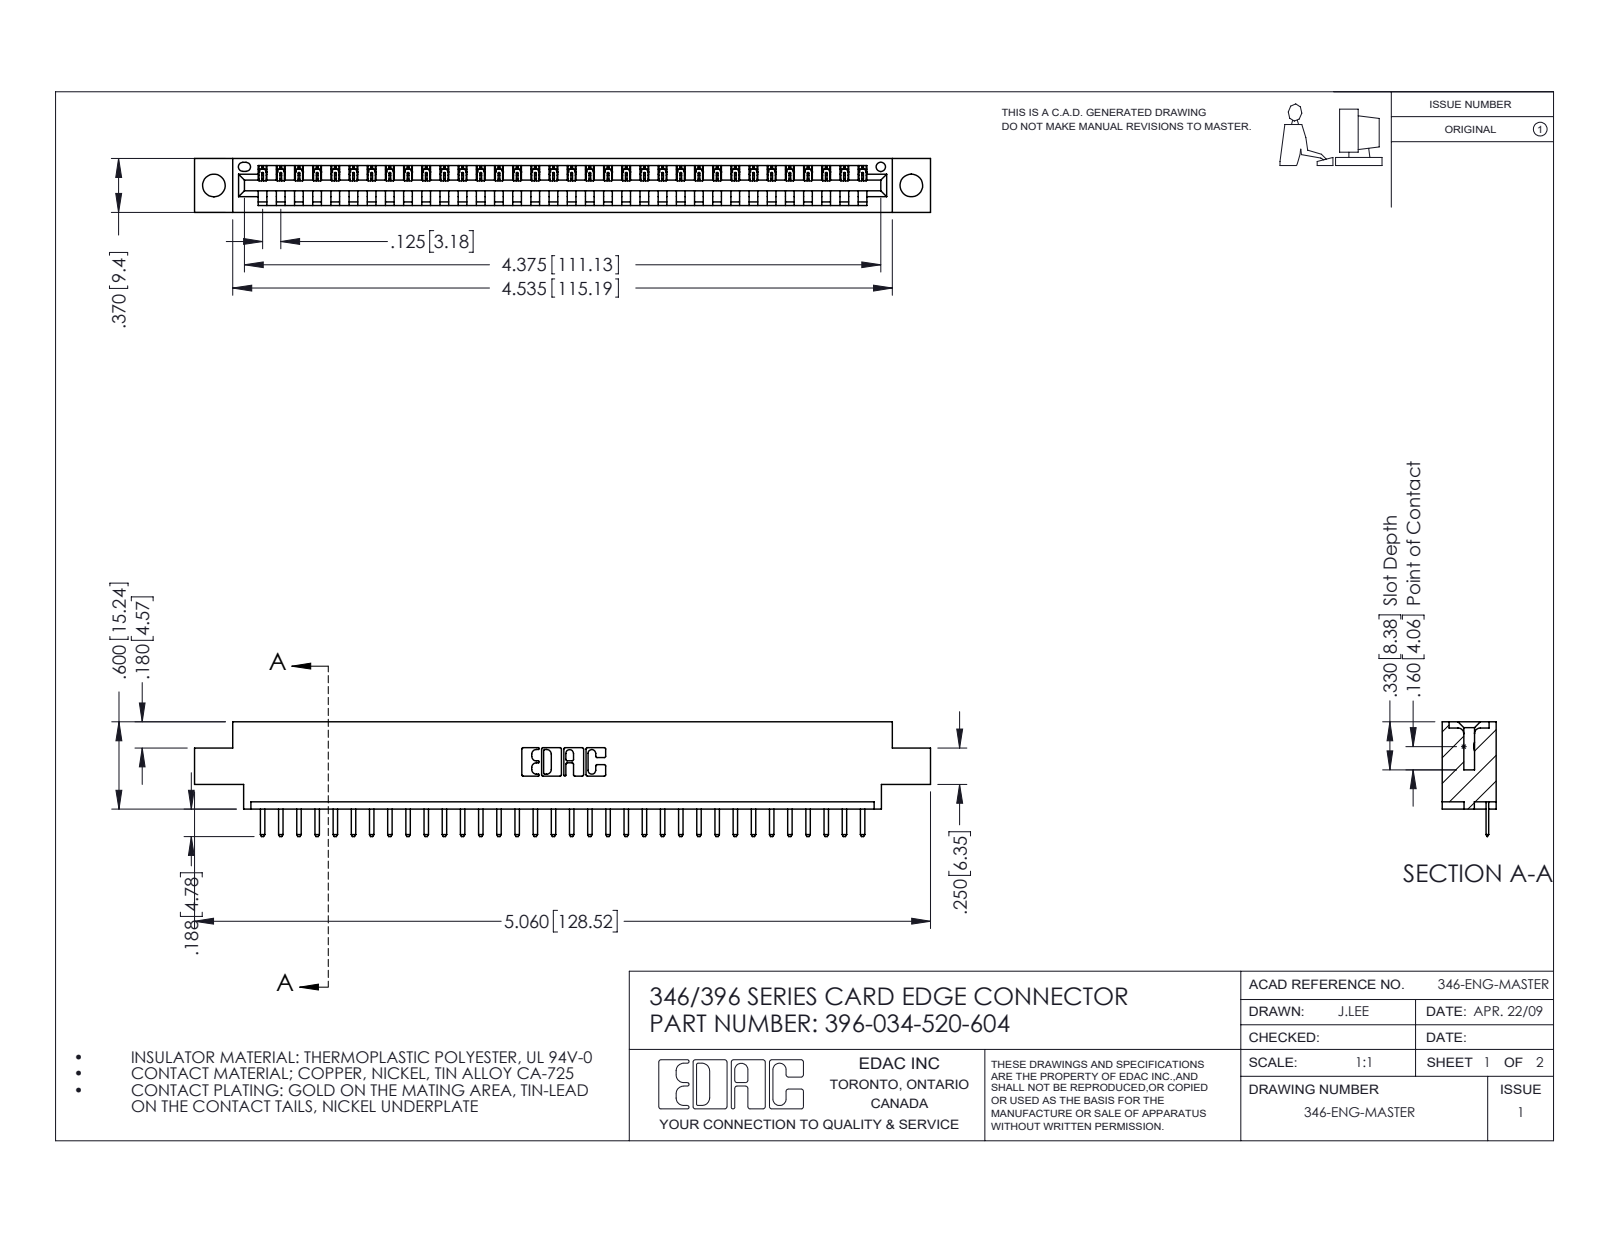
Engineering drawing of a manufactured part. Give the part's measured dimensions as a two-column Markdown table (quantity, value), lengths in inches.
| quantity | value |
| --- | --- |
| part name | 346 Part_0.170 Offset - 0.156 Dia-TH; 396-034-520-604; 345-292-001_345-293-120 |
| STEP written by | SolidWorks 2016 (CONFIG_CONTROL_DESIGN) |
| units | inches |
| bodies | 35 solids, 2234 faces (1508 planar, 726 cylindrical, 0 other) |
| overall size | 5.06 × 0.788 × 0.37 |
| volume | 0.727 in³ |
| surface area | 22.37 in² |
| round holes (diameter × count) | 0.156 × 2, 0.064 × 1 |
| partial cylindrical surfaces (radius × count) | 0.01 × 70, 0.006 × 68, 0.01 × 22, 0.007 × 6, 0.031 × 6, 0.026 × 3, 0.031 × 2, 0.04 × 2 |
| main face-to-face distances | 0.048, 0.322, 0.37, 0.25, 0.148, 0.222, 0.1, 0.174, 0.072, 0.298 |
| hole center spacings | 0.246, 4.587, 4.795 |
